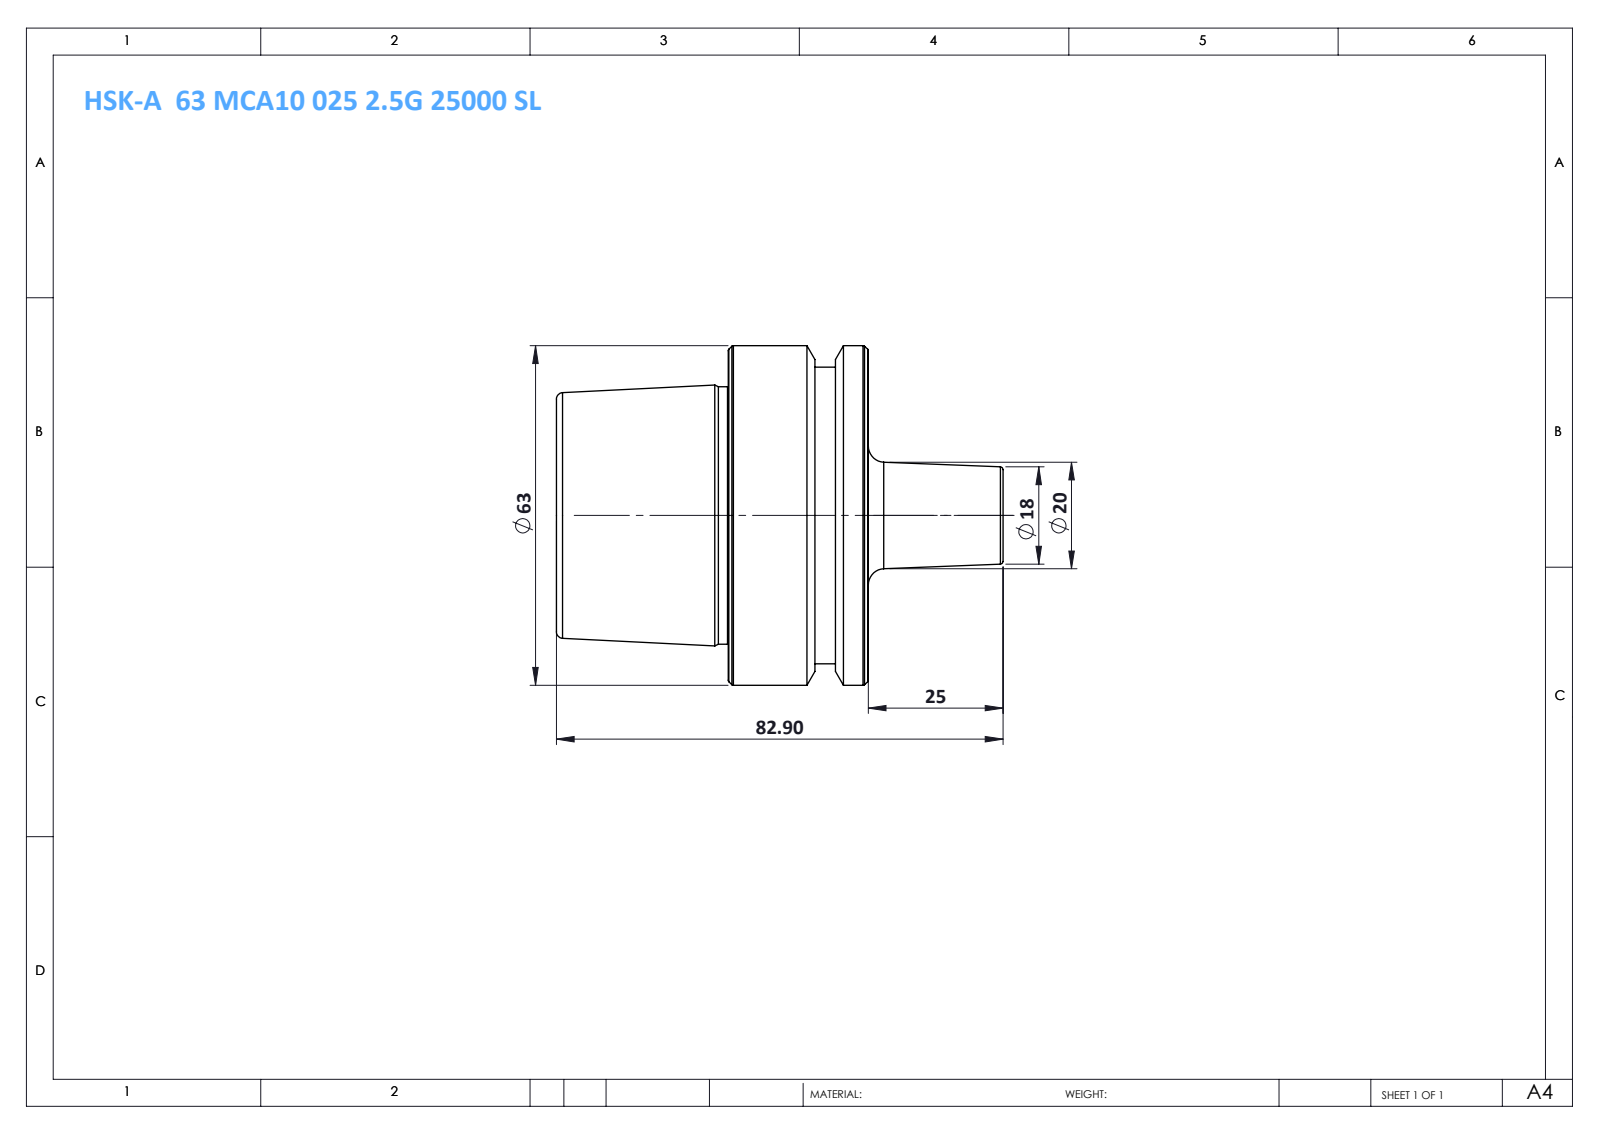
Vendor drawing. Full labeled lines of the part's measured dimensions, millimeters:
Part name (STEP PRODUCT): HSK-A 63 MCA10 025 2.5G 25000 SL
STEP written by: SolidWorks 2014 (CONFIG_CONTROL_DESIGN)
Units: millimetres
Bodies: 1 solid, 46 faces (6 planar, 8 cylindrical, 32 other)
Overall size (bounding box): 82.9 × 63 × 63
Volume: 139 805 mm³ · Surface area: 18 002 mm²
Round bosses / shafts (diameter × count): ⌀63 ×1, ⌀55 ×1, ⌀47.78 ×1
Main face-to-face distances: 57.9, 26, 31.9, 6.1, 19.9, 51.8, 9.9, 3.8, 16.1, 48
